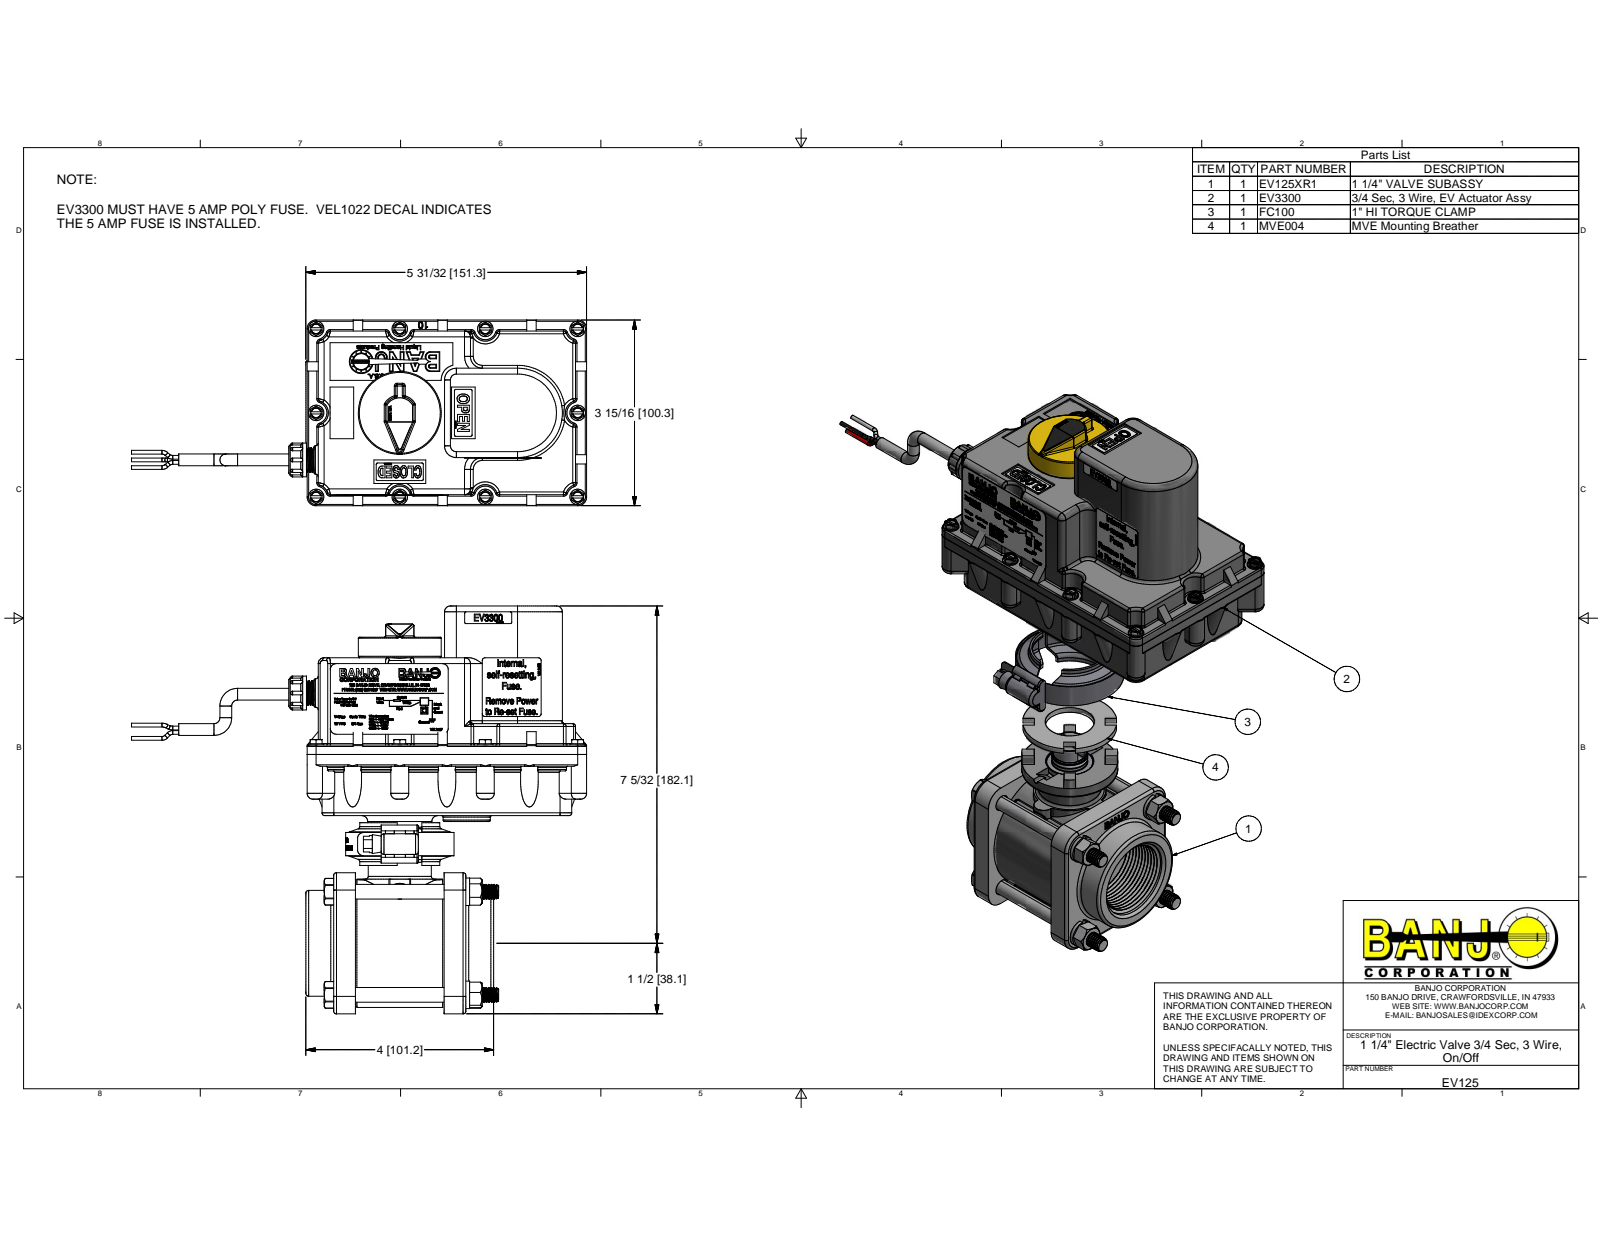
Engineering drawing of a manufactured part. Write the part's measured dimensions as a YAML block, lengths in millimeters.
part_name: "MEV10254AX; MEV10254A; VE10155SSH; MEV10151SS (+8 more)"
step_written_by: "Autodesk Inventor 2016 (AUTOMOTIVE_DESIGN)"
units: millimeters
bodies: {solids: 72, faces: 12630, planar: 6138, cylindrical: 1754, other: 4738}
overall_size: [245.27, 220.16, 100.33]
volume: 868080
surface_area: 395917
round_holes:
  - {diameter: 2.79, count: 10}
  - {diameter: 4.06, count: 10}
  - {diameter: 5.08, count: 10}
  - {diameter: 1.32, count: 8}
  - {diameter: 2.01, count: 8}
  - {diameter: 1.19, count: 6}
  - {diameter: 3.05, count: 6}
  - {diameter: 3.81, count: 6}
  - {diameter: 4.47, count: 6}
  - {diameter: 0.38, count: 4}
  - {diameter: 6.41, count: 4}
  - {diameter: 8.18, count: 4}
round_bosses_or_shafts:
  - {diameter: 6.82, count: 60}
  - {diameter: 8.33, count: 10}
  - {diameter: 3.51, count: 10}
  - {diameter: 2.03, count: 9}
  - {diameter: 2.62, count: 8}
  - {diameter: 6.35, count: 7}
  - {diameter: 1.9, count: 5}
  - {diameter: 14.81, count: 4}
partial_cylinders:
  - {radius: 0.76, count: 143}
  - {radius: 1.52, count: 79}
  - {radius: 0.51, count: 62}
  - {radius: 0.89, count: 43}
  - {radius: 3.17, count: 32}
  - {radius: 8, count: 24}
  - {radius: 12.7, count: 24}
  - {radius: 9.91, count: 16}
face_to_face_distances: [3.17, 3.18, 27.94, 5.08, 26.04, 19.81, 33.02, 82.04, 20.07, 76.96]
hole_center_spacings: [42.68, 52.27, 42.78, 45.34, 60.36, 2.77, 12.5, 30.18]
